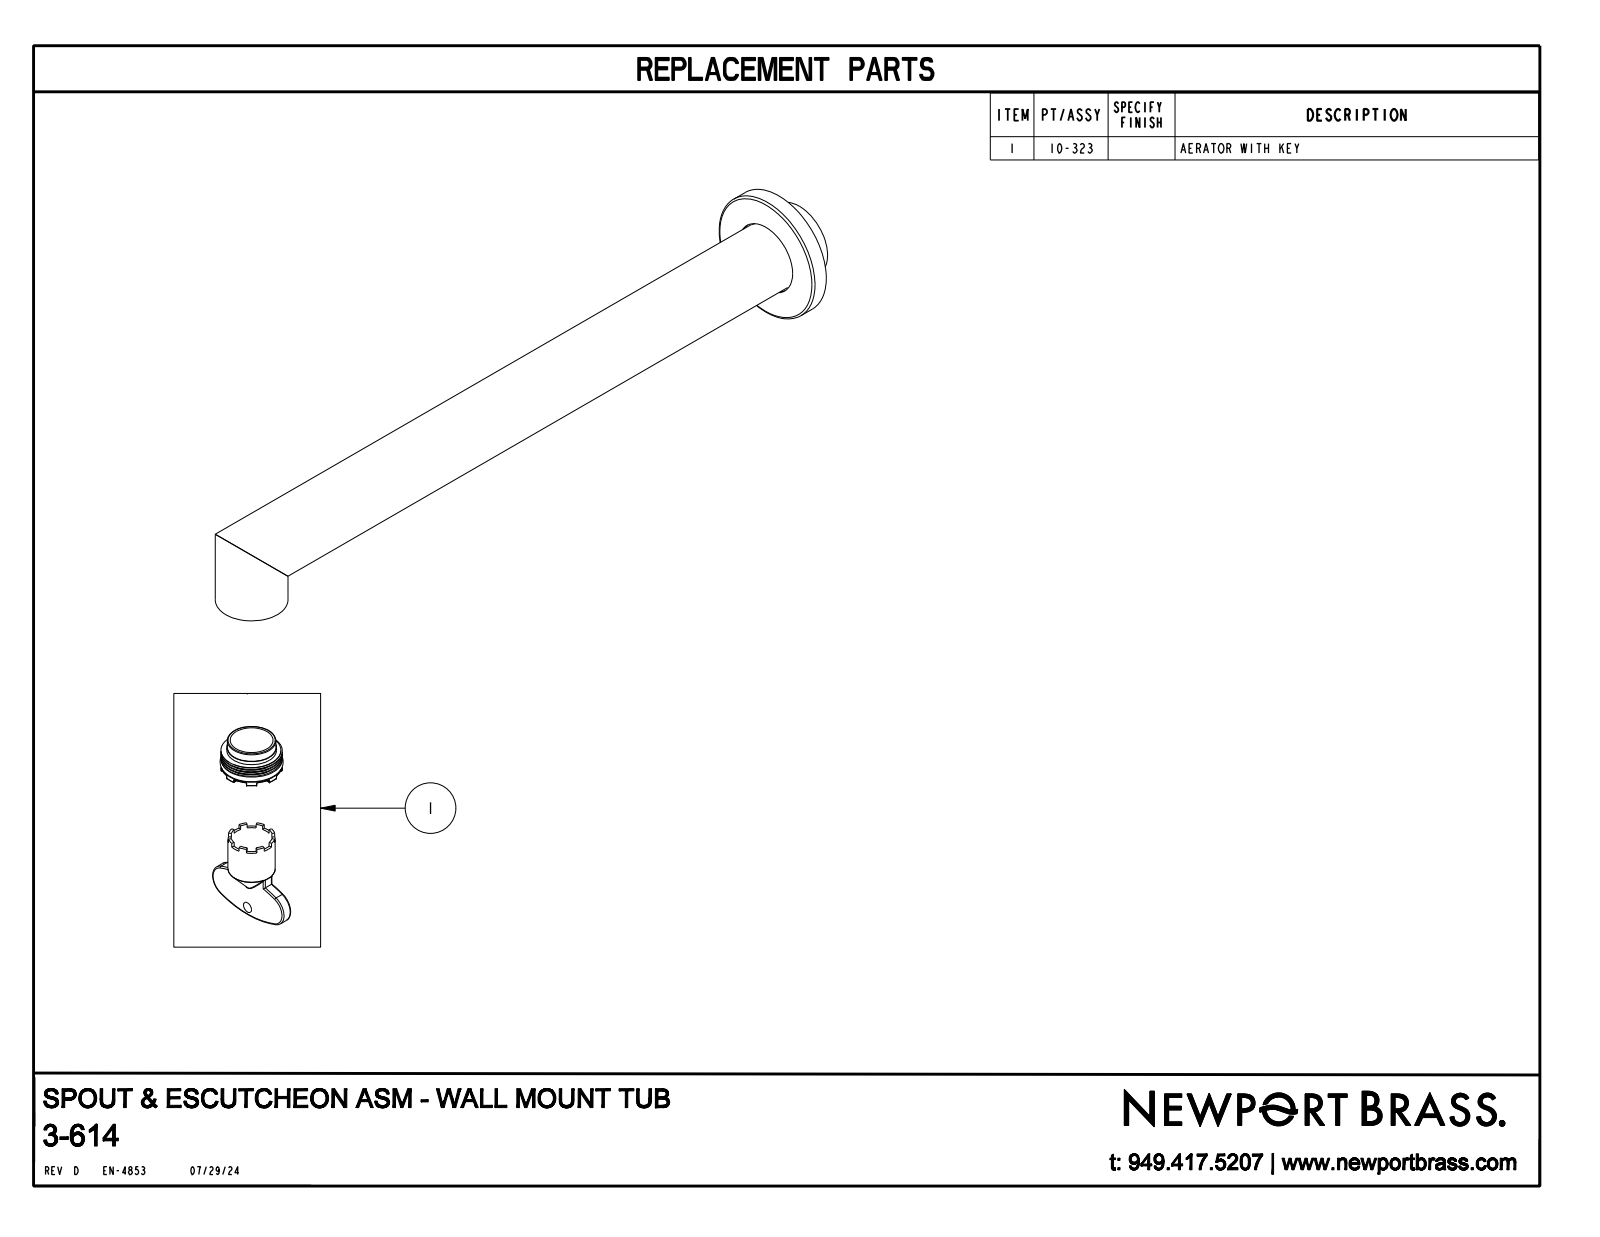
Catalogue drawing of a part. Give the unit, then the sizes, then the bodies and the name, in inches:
Units: inches
Overall size (bounding box): 11.15 × 1.85 × 1.85
Round bosses / shafts (diameter × count): ⌀1 ×2, ⌀1.85 ×1, ⌀1.1 ×1
Main face-to-face distances: 0.25, 0.4, 0.65
Volume: 9.495 in³ · Surface area: 42.52 in²
Bodies: 1 solid, 18 faces (6 planar, 8 cylindrical, 4 other)
Part name (STEP PRODUCT): 3-614
STEP written by: CREO PARAMETRIC BY PTC INC, 2018400 (AUTOMOTIVE_DESIGN)
